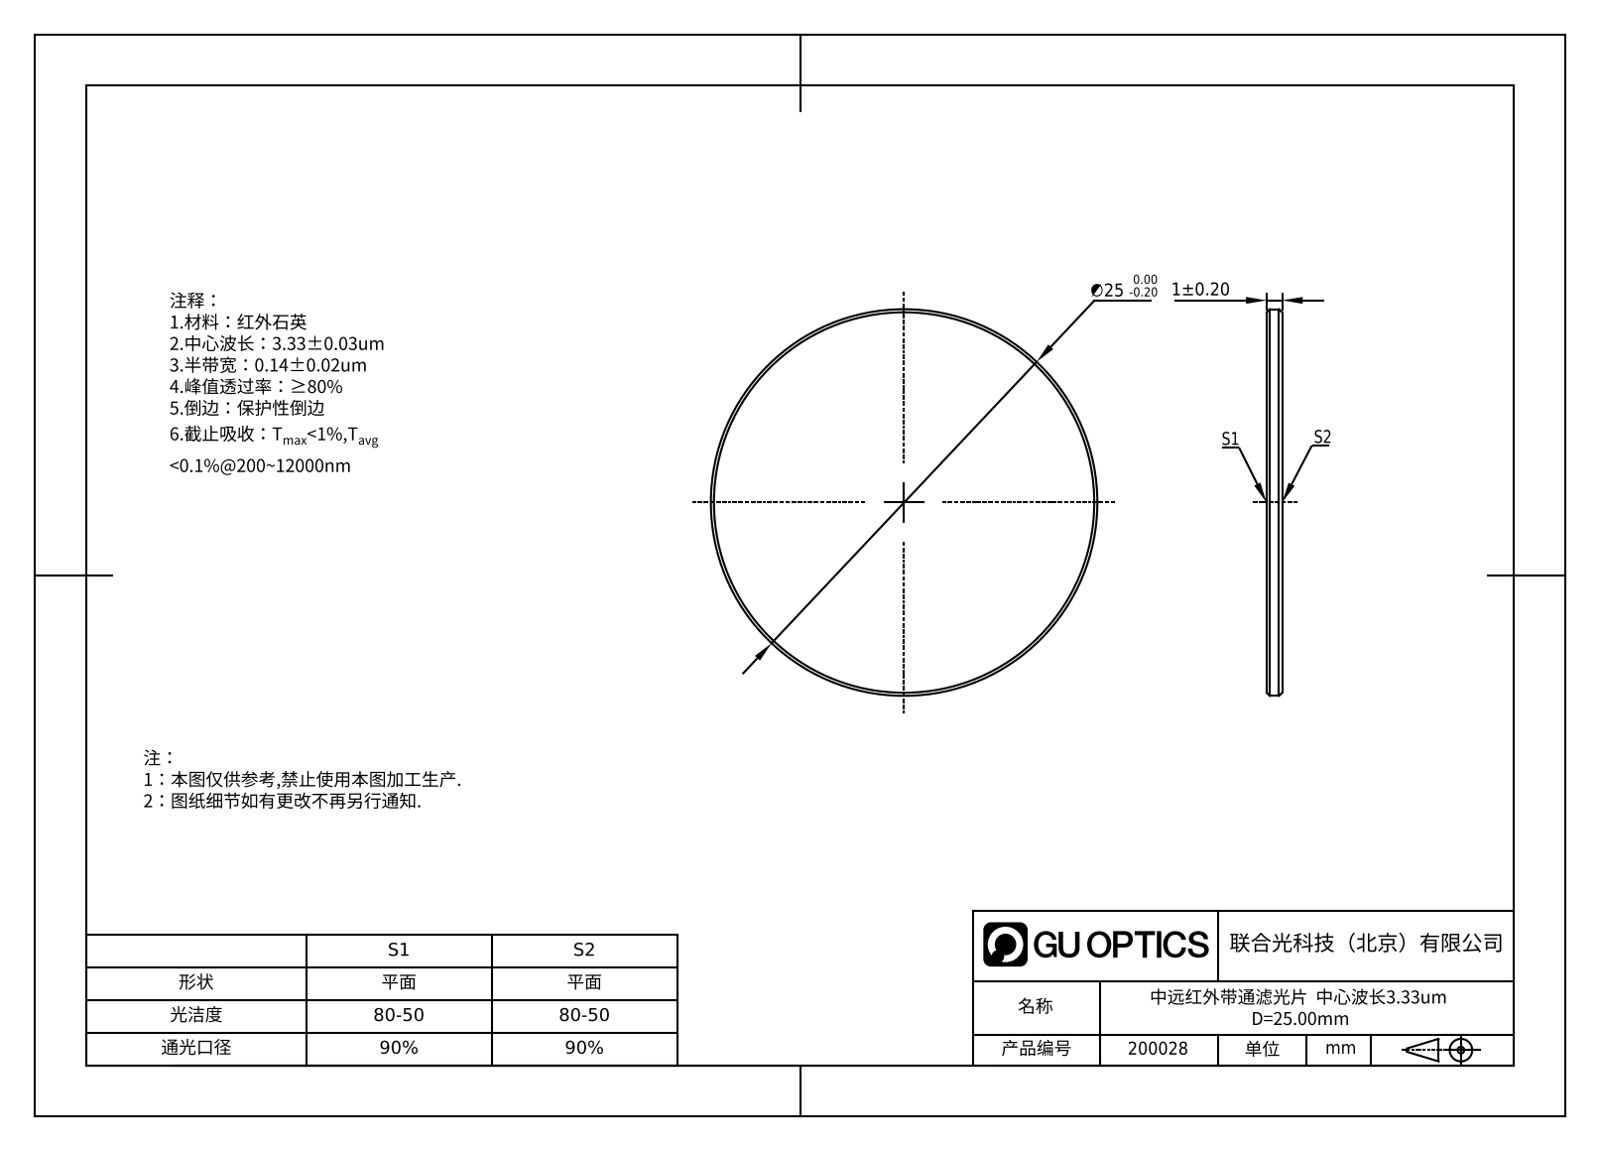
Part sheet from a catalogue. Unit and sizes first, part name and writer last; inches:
Units: inches
Overall size (bounding box): 0.984 × 0.984 × 0.039
Round bosses / shafts (diameter × count): ⌀0.984 ×1
Main face-to-face distances: 0.039
Volume: 0.03 in³ · Surface area: 1.615 in²
Bodies: 1 solid, 8 faces (2 planar, 2 cylindrical, 4 other)
Part name (STEP PRODUCT): GNIF-140-3330-D25
STEP written by: SolidWorks 2022 (AUTOMOTIVE_DESIGN)
